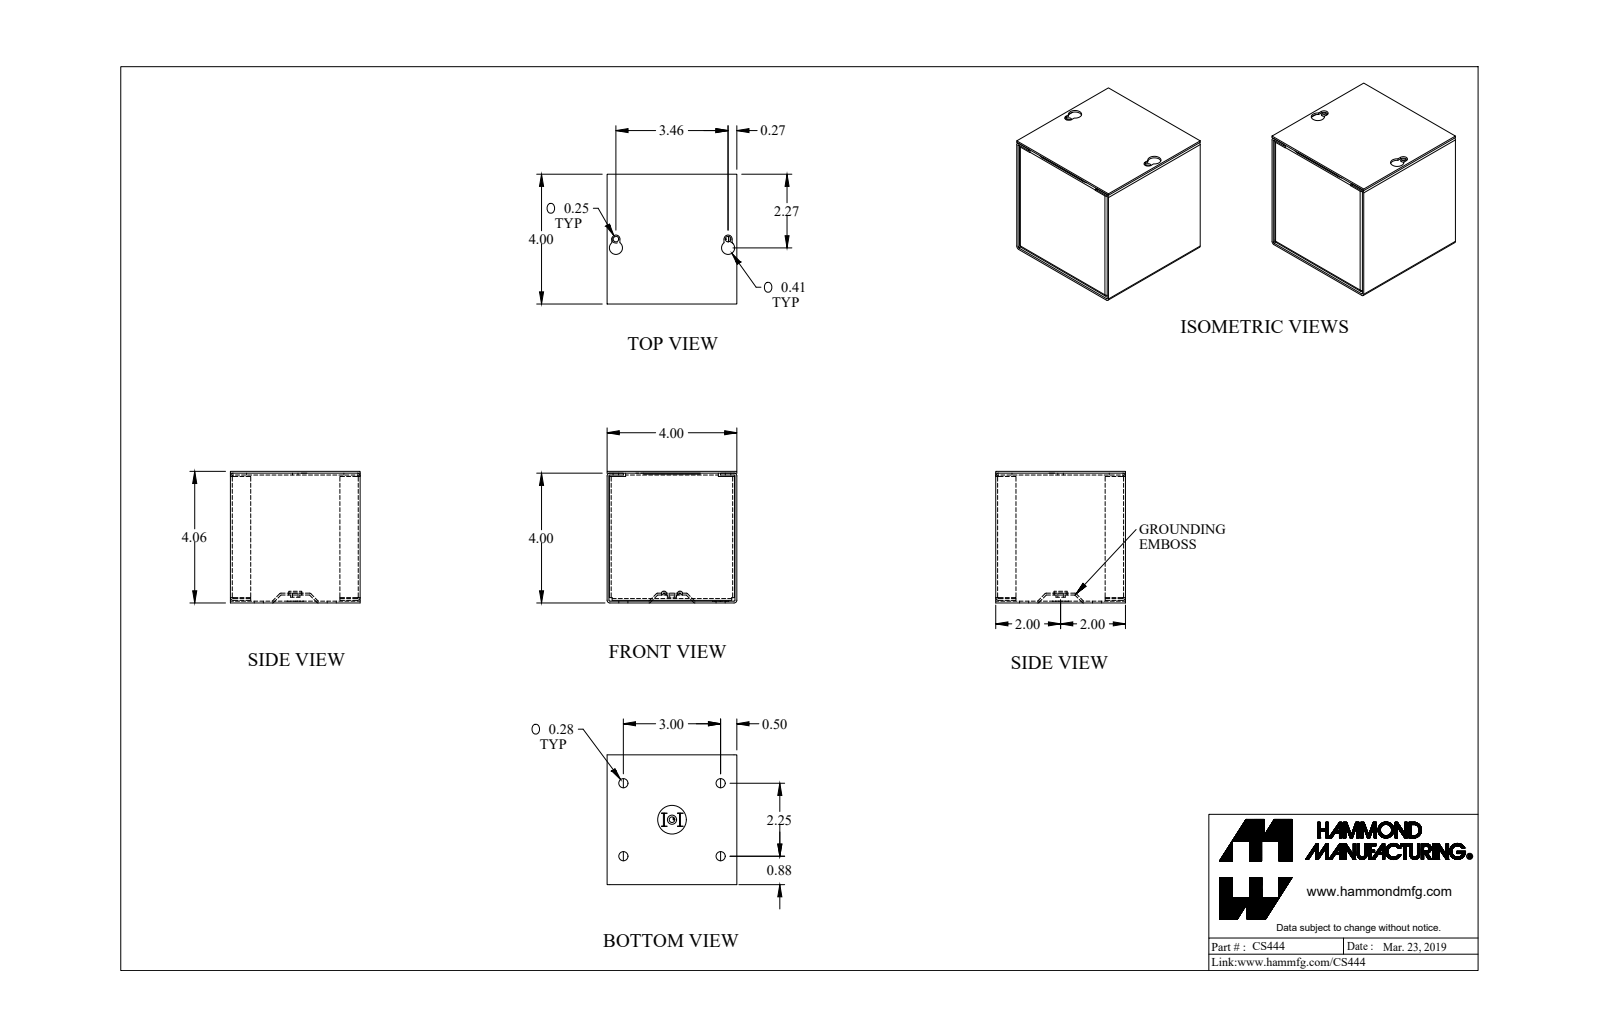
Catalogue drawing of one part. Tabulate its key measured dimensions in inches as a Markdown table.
| quantity | value |
| --- | --- |
| part name | CS444_Default |
| STEP written by | SolidWorks 2019 (CONFIG_CONTROL_DESIGN) |
| units | inches |
| bodies | 4 solids, 189 faces (121 planar, 60 cylindrical, 8 other) |
| overall size | 4.057 × 4 × 4 |
| volume | 6.329 in³ |
| surface area | 227.7 in² |
| round holes (diameter × count) | 0.281 × 4, 0.17 × 3, 0.5 × 1 |
| round bosses / shafts (diameter × count) | 0.492 × 1, 0.284 × 1 |
| partial cylindrical surfaces (radius × count) | 0.029 × 12, 0.086 × 12, 0.057 × 8, 0.125 × 2, 0.203 × 2 |
| main face-to-face distances | 0.057, 3.943, 4, 3.886, 0.07, 3.873, 4.057, 0.127, 3.816, 3.93 |
| hole center spacings | 1.148, 1.875, 3.42, 1.125, 1.73, 2.25, 3, 3.204 |
